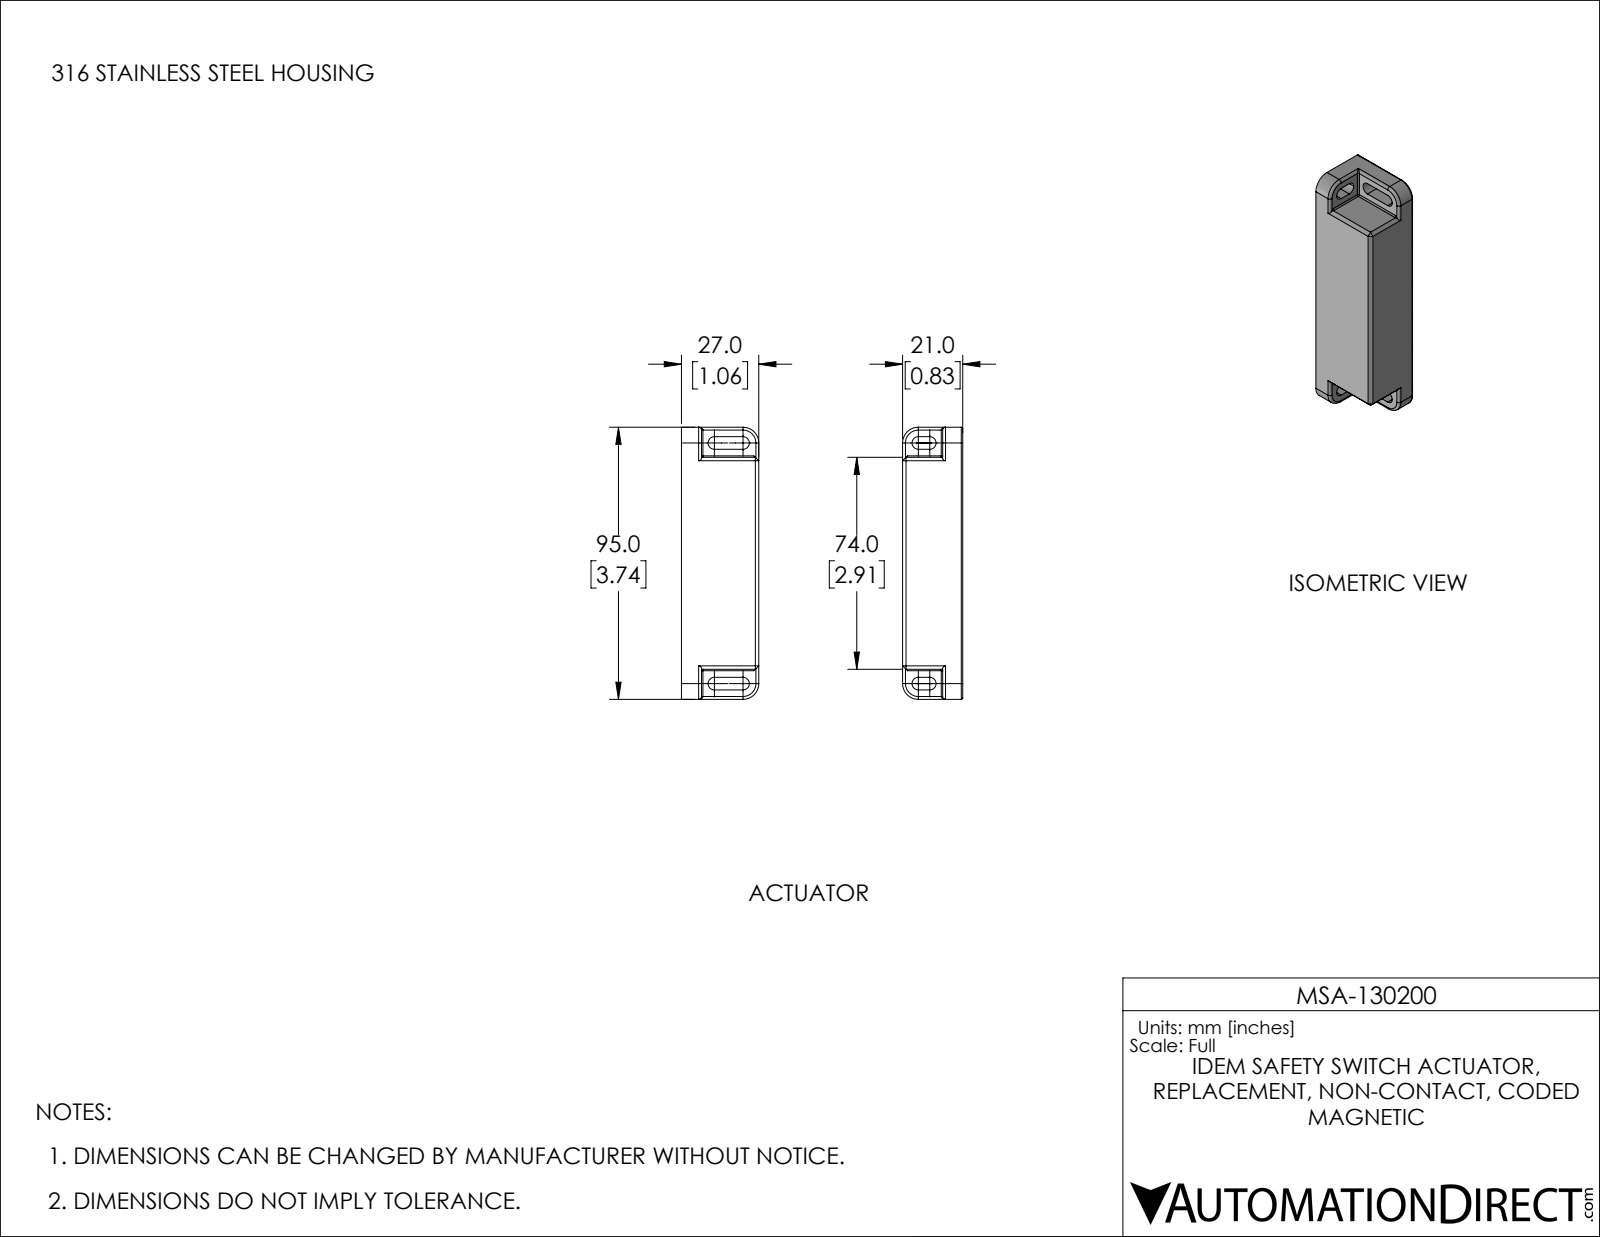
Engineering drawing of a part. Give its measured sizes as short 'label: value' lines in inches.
name: 130-MSA-Actuator
written by: SolidWorks 2019 (AUTOMOTIVE_DESIGN)
unit: in
bodies: 1 solid, 278 faces (105 planar, 104 cylindrical, 69 other)
size: 3.74 × 1.063 × 0.827
volume: 1.235 in³; area: 27.67 in²
bosses: 1× ⌀0.197, 1× ⌀0.079
rounds: 47× R0.02, 8× R0.012, 8× R0.089, 6× R0.039, 5× R0.079, 4× R0.008, 4× R0.217
face distances: 0.079, 0.748, 0.827, 0.669, 1.047, 0.016, 0.969, 0.059, 0.909, 0.988
